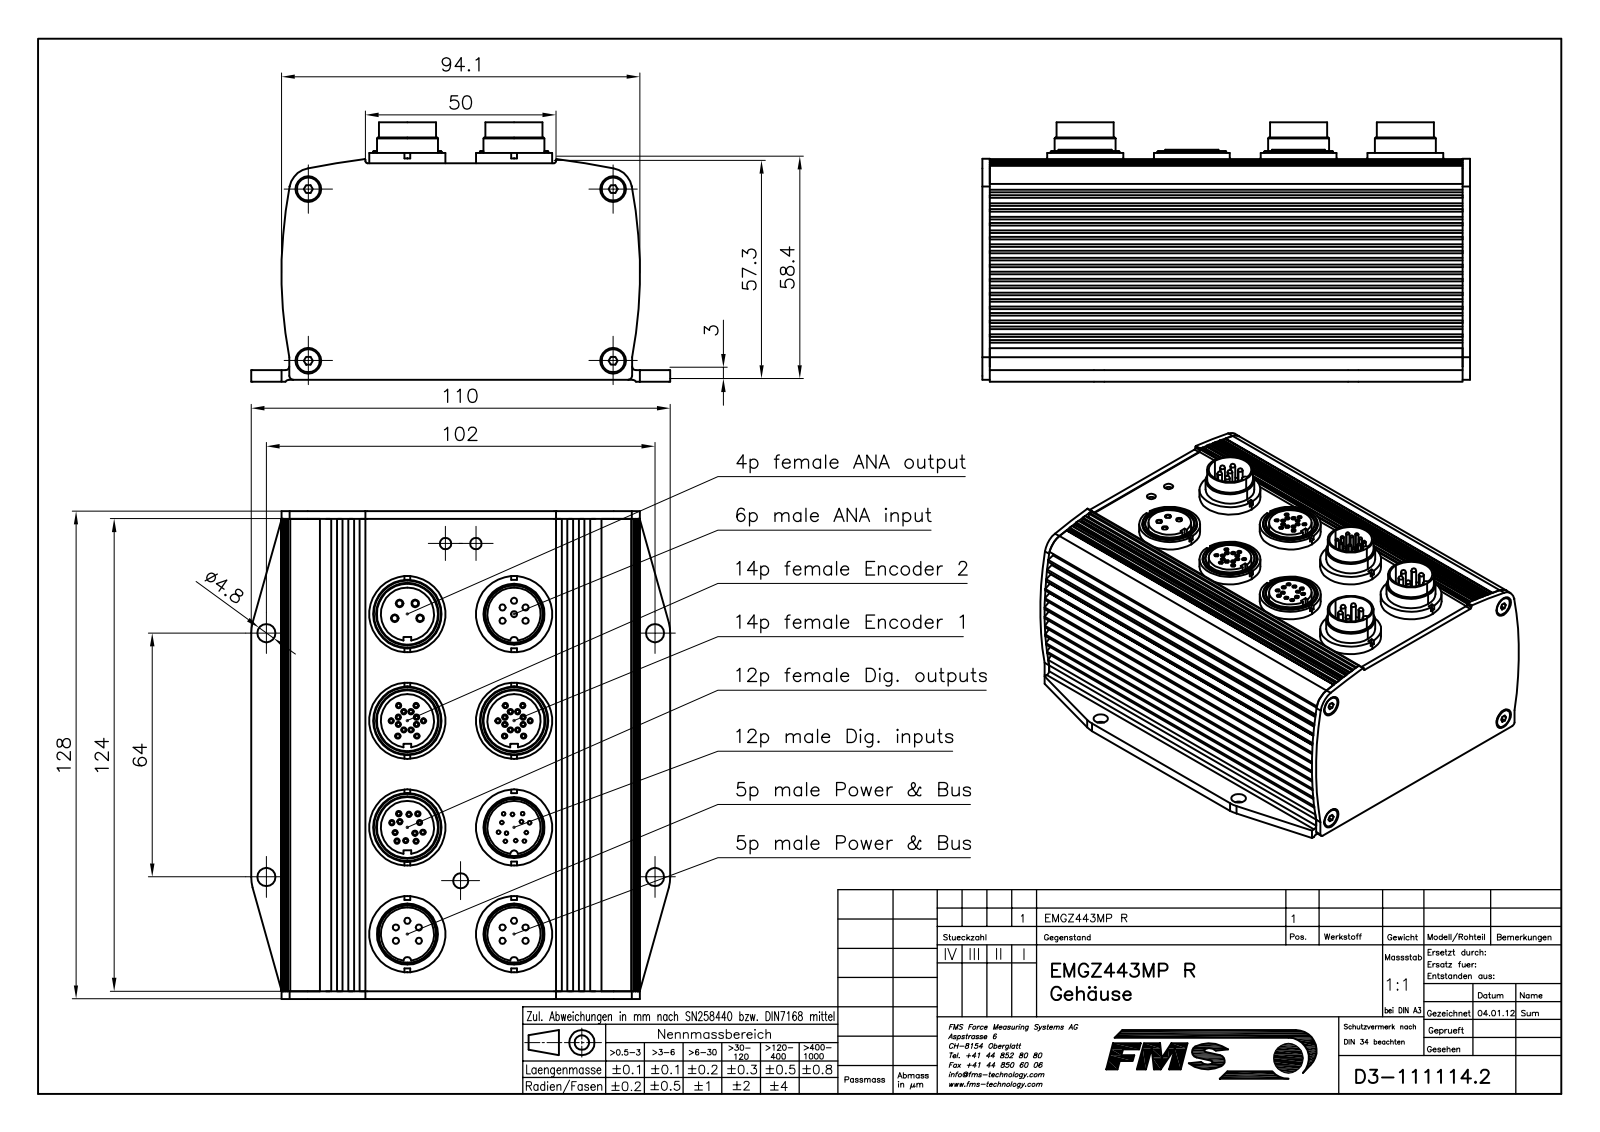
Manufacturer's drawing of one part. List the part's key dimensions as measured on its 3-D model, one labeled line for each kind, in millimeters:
Part name (STEP PRODUCT): E1111142; E1111143; EINPRESSGEWINDEBOLZEN_M4X10; FLANSCHSTECKER_09-0115-89-05 (+8 more)
STEP written by: Mechanical Desktop 2009 (CONFIG_CONTROL_DESIGN)
Units: millimetres
Bodies: 36 solids, 1692 faces (593 planar, 831 cylindrical, 268 other)
Overall size (bounding box): 128 × 110 × 68
Volume: 148 960 mm³ · Surface area: 127 426 mm²
Round holes (diameter × count): ⌀0.6 ×52, ⌀1 ×40, ⌀16 ×8, ⌀2.6 ×5, ⌀1.6 ×4, ⌀3.2 ×4, ⌀4.8 ×4, ⌀14 ×4, ⌀18 ×4, ⌀3 ×2, ⌀4 ×1
Round bosses / shafts (diameter × count): ⌀0.7 ×52, ⌀1.1 ×20, ⌀1.6 ×16, ⌀1 ×12, ⌀20 ×8, ⌀18 ×4, ⌀16.4 ×4, ⌀15 ×4
Partial cylindrical surfaces — rounded edges, fillets, slot ends (radius × count): R0.25 ×70, R2 ×44, R1 ×10, R9.02 ×8, R10 ×4, R0.2 ×2, R0.5 ×2, R3 ×2
Main face-to-face distances: 2, 54.5, 126, 52.5, 124, 56.5, 128, 2.5, 0.5, 1.5
Hole centre spacings: 5, 2.12, 7.3, 8, 39.6, 2.3, 3.09, 4.27
